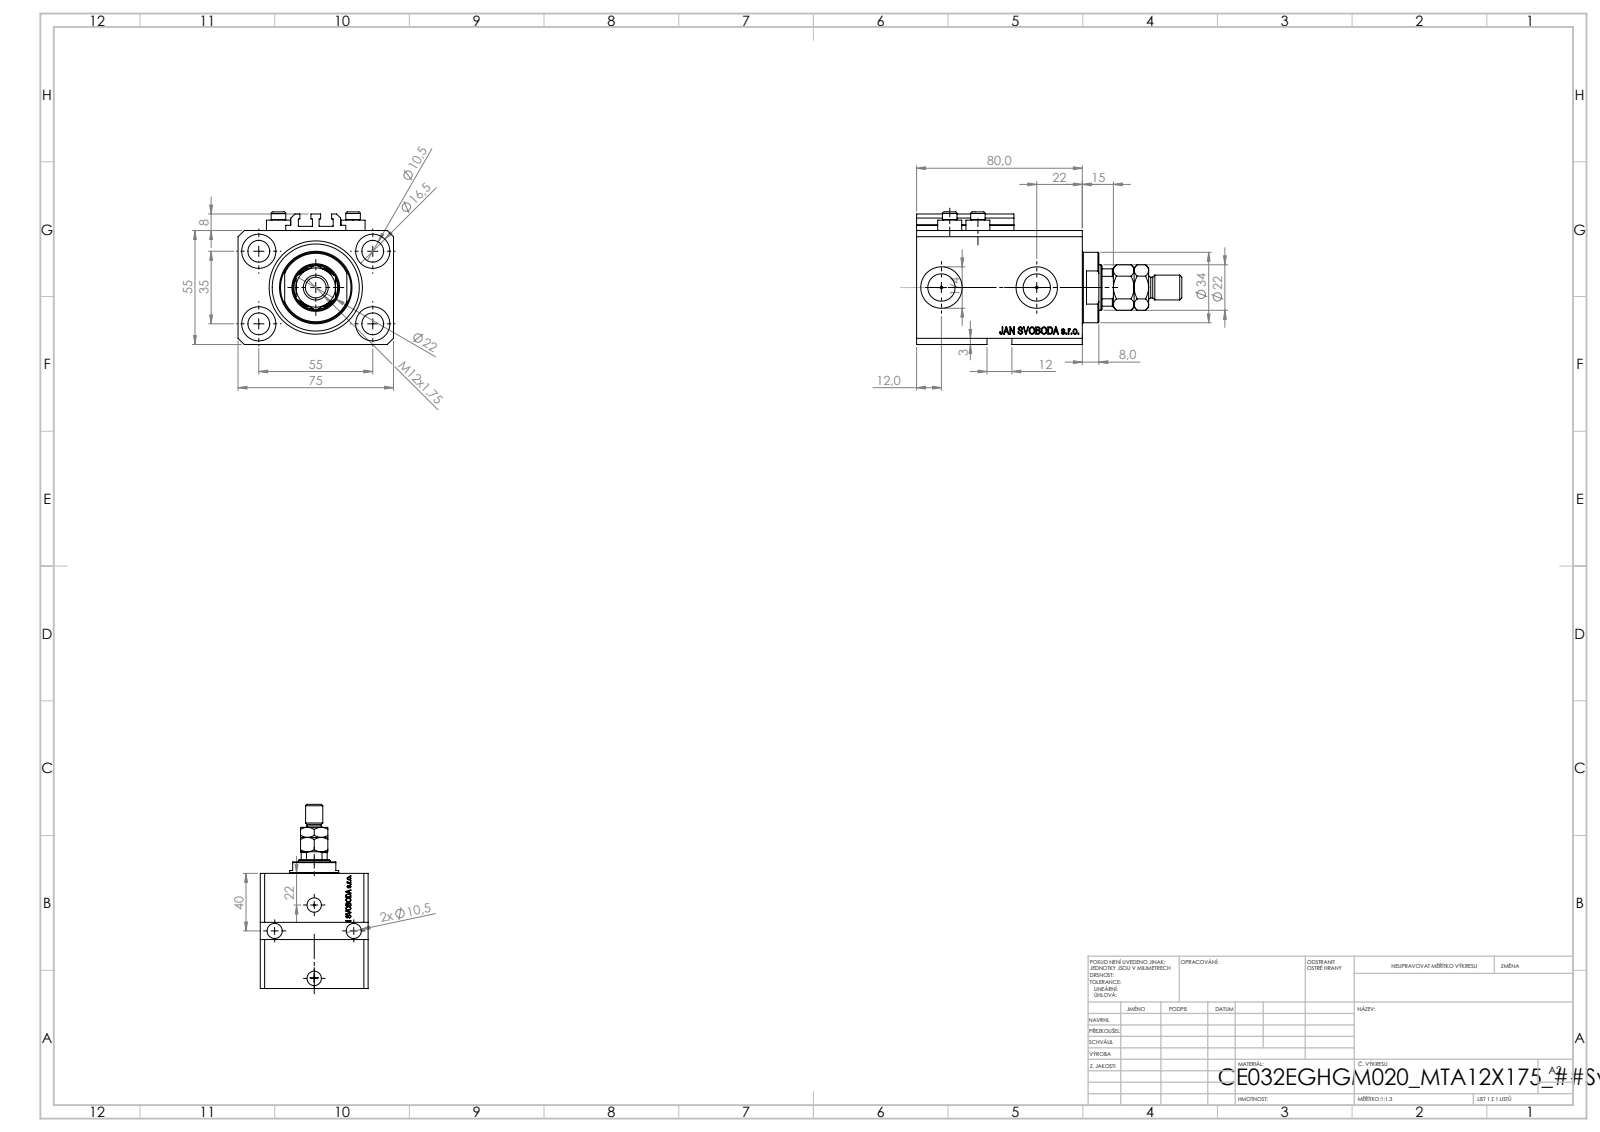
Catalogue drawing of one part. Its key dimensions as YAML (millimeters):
part_name: "MTA; V250CE_E_Body; V250CE_VC_E; V250CE_C_VCP (+1 more)"
step_written_by: "SolidWorks 2019 (CONFIG_CONTROL_DESIGN)"
units: millimeters
bodies: {solids: 9, faces: 1113, planar: 529, cylindrical: 130, other: 454}
overall_size: [128, 75, 64]
volume: 290869
surface_area: 76781
round_holes:
  - {diameter: 10.5, count: 7}
  - {diameter: 1.25, count: 4}
  - {diameter: 4, count: 4}
  - {diameter: 16.5, count: 4}
  - {diameter: 10, count: 2}
  - {diameter: 13.16, count: 2}
  - {diameter: 20, count: 2}
  - {diameter: 22, count: 1}
  - {diameter: 32, count: 1}
  - {diameter: 45, count: 1}
round_bosses_or_shafts:
  - {diameter: 11.6, count: 4}
  - {diameter: 7, count: 4}
  - {diameter: 34, count: 1}
  - {diameter: 12, count: 1}
  - {diameter: 10, count: 1}
partial_cylinders:
  - {radius: 0.2, count: 10}
  - {radius: 10.5, count: 1}
face_to_face_distances: [55, 75, 15, 65, 80, 3, 55.1, 9.9, 70.1, 54]
hole_center_spacings: [32.6, 55, 13.6, 14.09, 19.89, 20.12, 25.81, 28.48]
